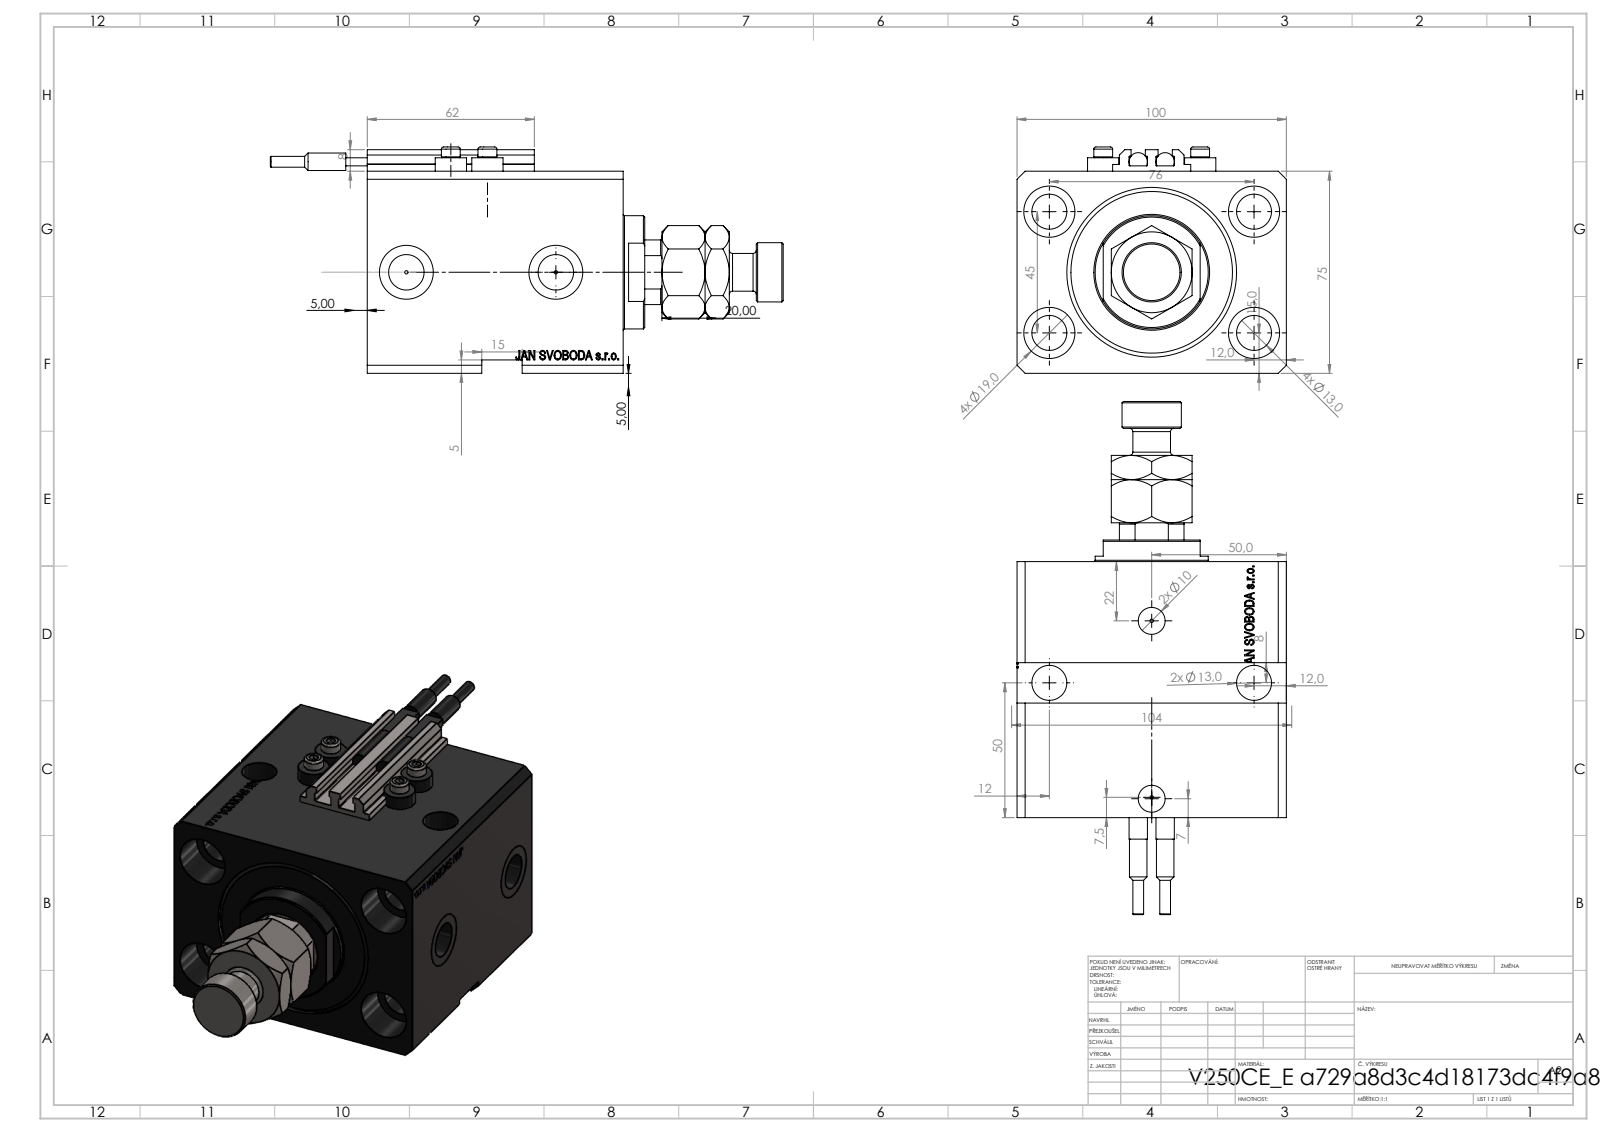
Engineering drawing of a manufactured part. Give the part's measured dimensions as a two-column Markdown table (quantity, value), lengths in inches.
| quantity | value |
| --- | --- |
| part name | SWITCH_V250CE; V250CE_VC_E; V250CE_E; MFA (+2 more) |
| STEP written by | SolidWorks 2019 (CONFIG_CONTROL_DESIGN) |
| units | inches |
| bodies | 11 solids, 1208 faces (587 planar, 154 cylindrical, 467 other) |
| overall size | 7.496 × 3.937 × 3.307 |
| volume | 38.58 in³ |
| surface area | 205.4 in² |
| round holes (diameter × count) | 0.512 × 6, 0.049 × 4, 0.157 × 4, 0.748 × 4, 0.394 × 2, 0.518 × 2, 0.787 × 2, 0.728 × 1, 1.102 × 1, 1.969 × 1, 2.48 × 1 |
| round bosses / shafts (diameter × count) | 0.457 × 4, 0.276 × 4, 0.268 × 2, 0.256 × 2, 0.157 × 2, 1.654 × 1, 0.866 × 1, 0.551 × 1 |
| partial cylindrical surfaces (radius × count) | 0.008 × 10, 0.531 × 1 |
| main face-to-face distances | 2.953, 3.937, 3.74, 0.469, 3.272, 2.693, 2.224, 1.047, 0.197, 0.118 |
| hole center spacings | 1.739, 2.992, 0.535, 0.816, 1.086, 1.165, 1.181, 1.324 |
